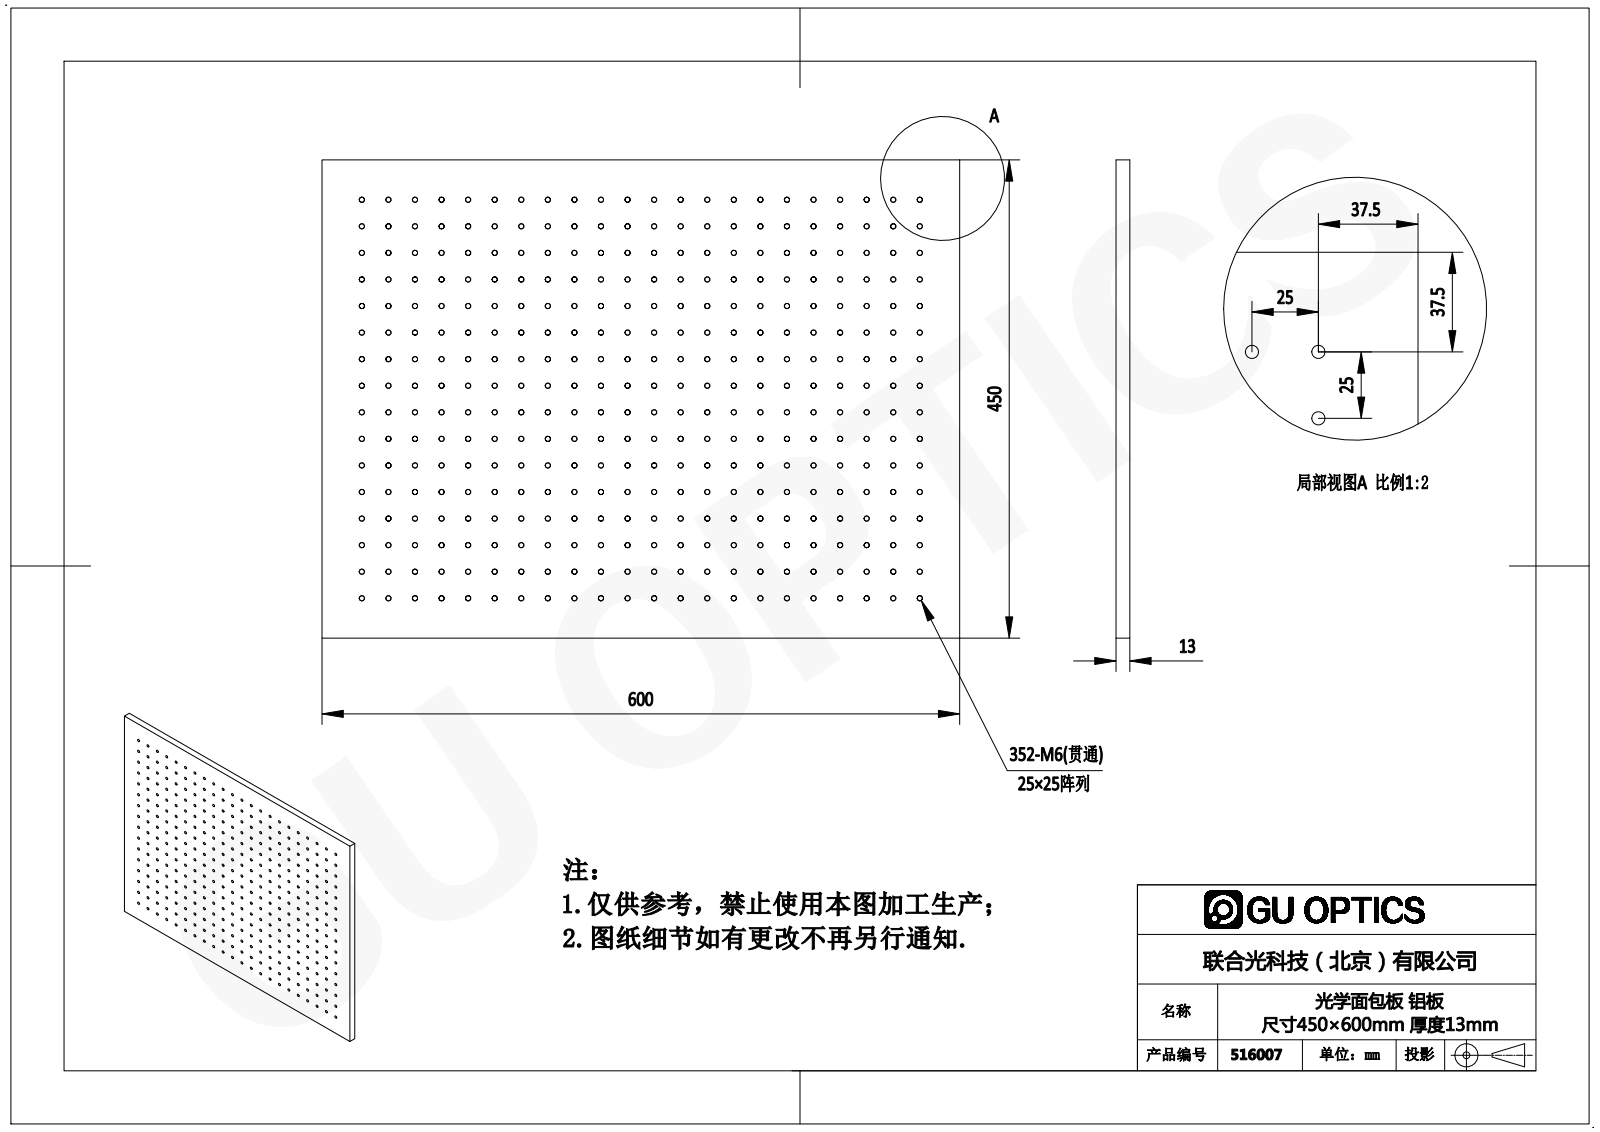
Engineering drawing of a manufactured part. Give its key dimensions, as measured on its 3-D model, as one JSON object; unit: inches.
{"part_name": "516007", "step_written_by": "SolidWorks 2016 (AUTOMOTIVE_DESIGN)", "units": "inches", "bodies": {"solids": 1, "faces": 710, "planar": 6, "cylindrical": 704, "other": 0}, "overall_size": [23.622, 17.717, 0.512], "volume_in3": 208.7, "surface_area_in2": 969.3, "round_holes": [[0.197, 352]], "face_to_face_distances": [0.512, 17.717, 23.622], "hole_center_spacings": [0.984, 1.392, 2.201, 1.969, 3.113, 2.953, 4.058, 3.937]}
